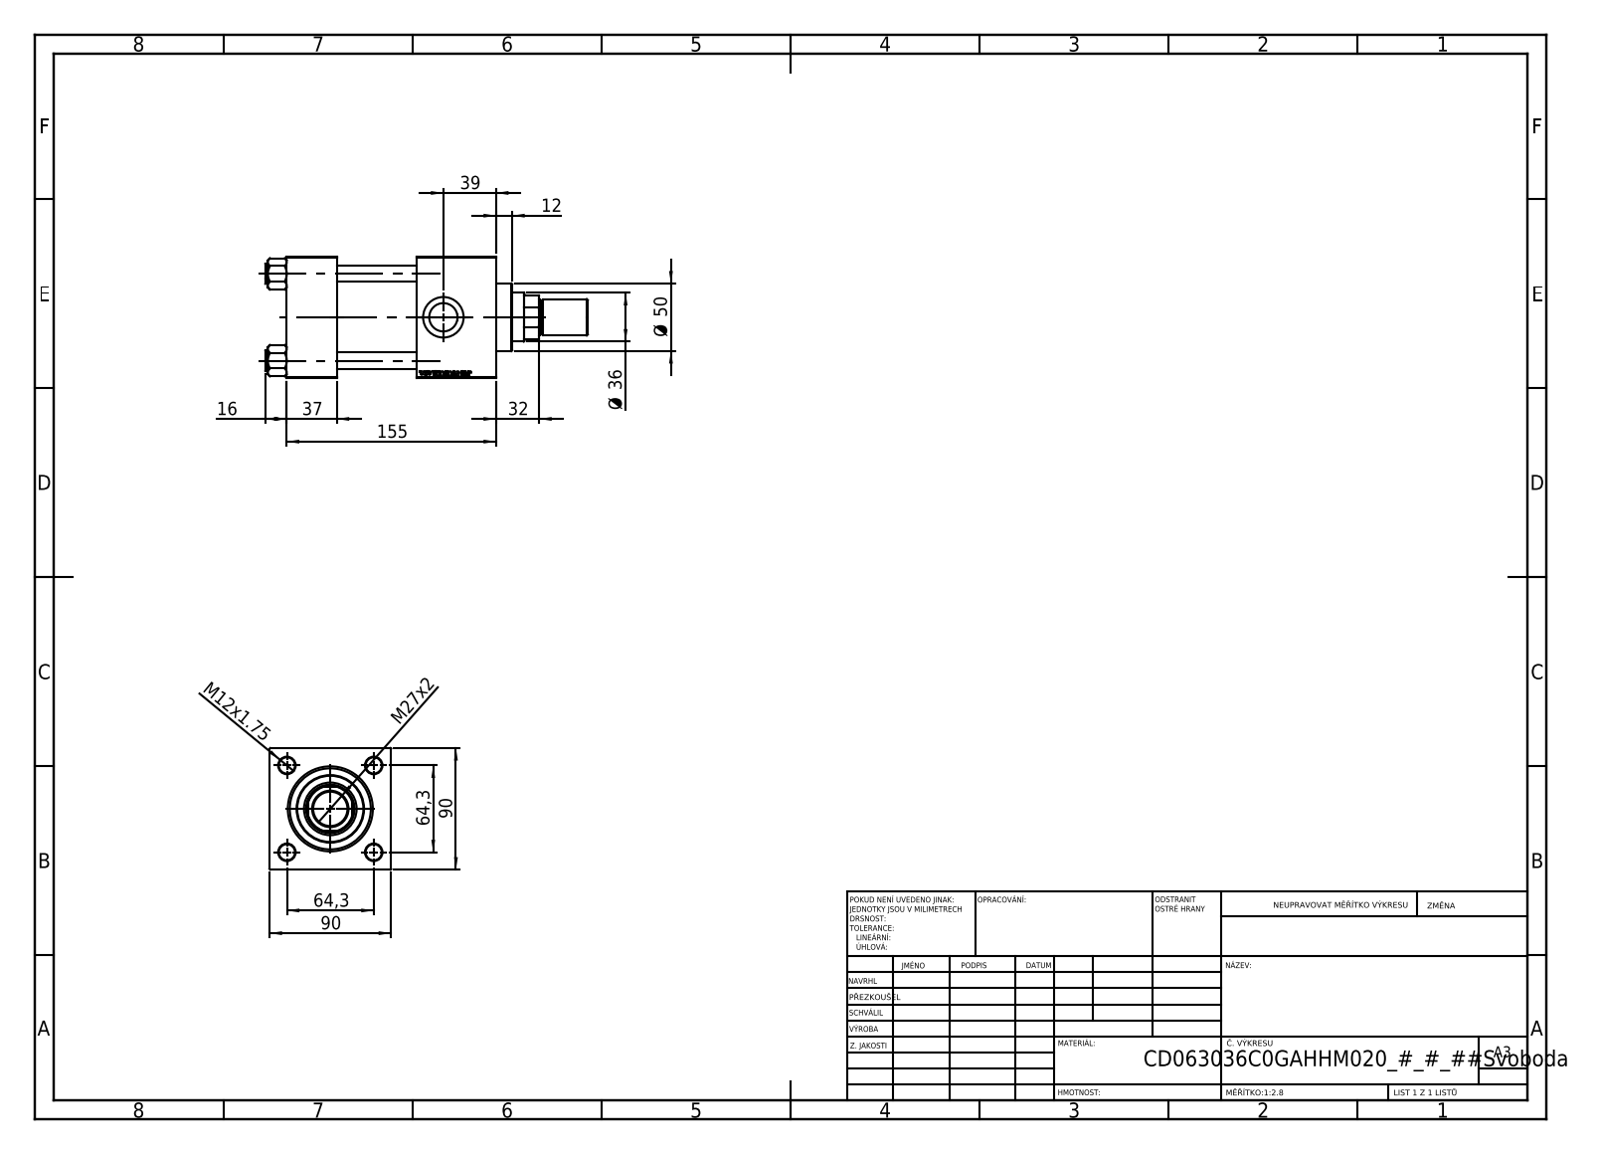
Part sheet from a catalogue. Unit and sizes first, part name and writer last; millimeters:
Units: millimetres
Overall size (bounding box): 239 × 90 × 90
Round holes (diameter × count): ⌀12 ×4, ⌀7 ×2, ⌀20.96 ×2, ⌀30 ×2, ⌀25.5 ×1, ⌀36 ×1, ⌀39 ×1, ⌀50 ×1, ⌀60 ×1, ⌀63 ×1
Round bosses / shafts (diameter × count): ⌀15 ×4, ⌀69 ×1, ⌀27 ×1, ⌀25 ×1
Partial cylindrical surfaces — rounded edges, fillets, slot ends (radius × count): R17.5 ×1
Main face-to-face distances: 90, 59, 37, 155, 118, 96, 20, 126.3, 89.3, 30.3
Hole centre spacings: 45.47, 64.3, 90.93
Volume: 988 249 mm³ · Surface area: 188 505 mm²
Bodies: 12 solids, 1163 faces (530 planar, 91 cylindrical, 542 other)
Part name (STEP PRODUCT): V215CD_VCP_C; V215CD_VC_C; V215CD_Body_C; ROD_END_AH (+2 more)
STEP written by: SolidWorks 2019 (CONFIG_CONTROL_DESIGN)
